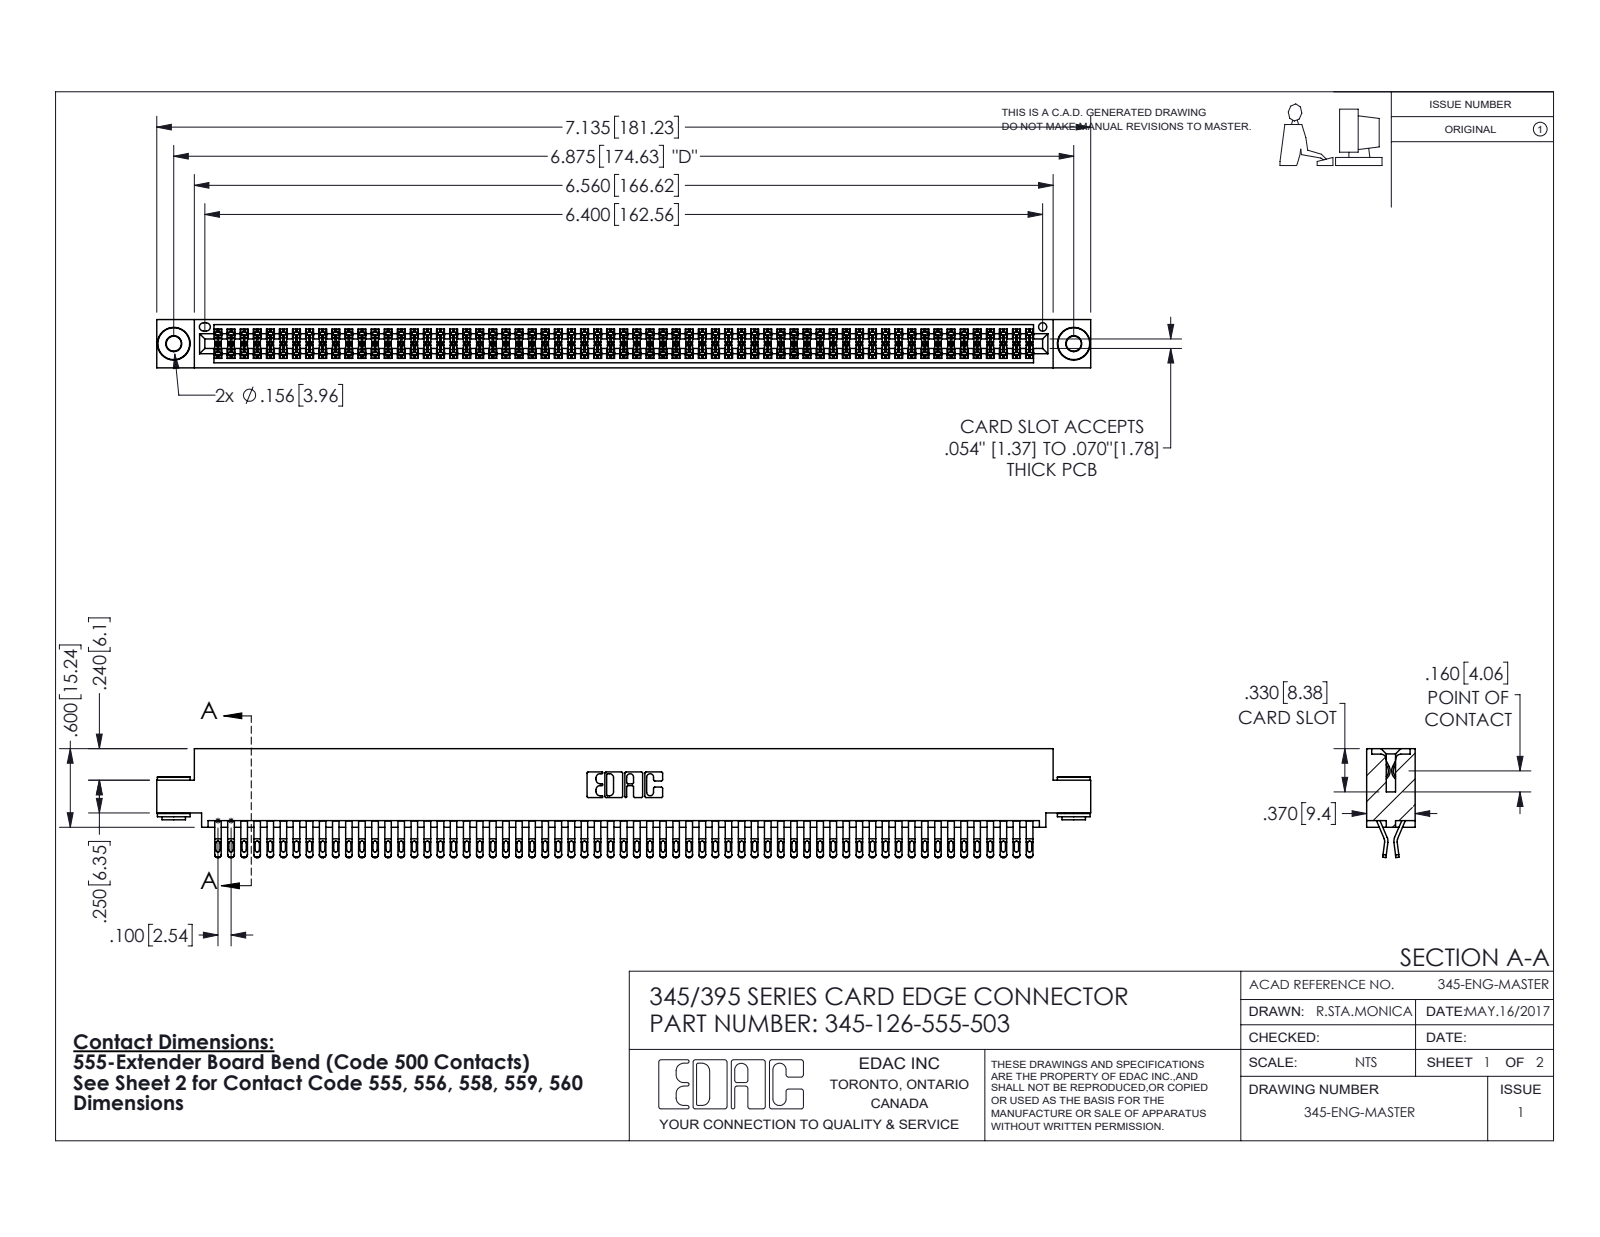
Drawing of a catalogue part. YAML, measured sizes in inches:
part_name: "345-250-002_345-250-002-102; 345-292-001_555 Tail; 345 Part_0.110 Offset - 0.156 Dia-TH; 345-126-555-503"
step_written_by: "SolidWorks 2016 (CONFIG_CONTROL_DESIGN)"
units: inches
bodies: {solids: 129, faces: 7224, planar: 4000, cylindrical: 3216, other: 8}
overall_size: [7.135, 0.832, 0.37]
volume: 1.105
surface_area: 44.56
round_holes:
  - {diameter: 0.116, count: 2}
  - {diameter: 0.156, count: 2}
  - {diameter: 0.064, count: 1}
round_bosses_or_shafts:
  - {diameter: 0.25, count: 2}
  - {diameter: 0.18, count: 2}
  - {diameter: 0.136, count: 2}
partial_cylinders:
  - {radius: 0.016, count: 315}
  - {radius: 0.02, count: 252}
  - {radius: 0.006, count: 189}
  - {radius: 0.01, count: 22}
  - {radius: 0.007, count: 6}
  - {radius: 0.031, count: 6}
  - {radius: 0.026, count: 3}
  - {radius: 0.01, count: 2}
face_to_face_distances: [0.072, 0.298, 0.025, 0.37, 0.2, 0.098, 0.272, 0.225, 0.175, 0.149]
hole_center_spacings: [0.27, 6.639, 6.875]
